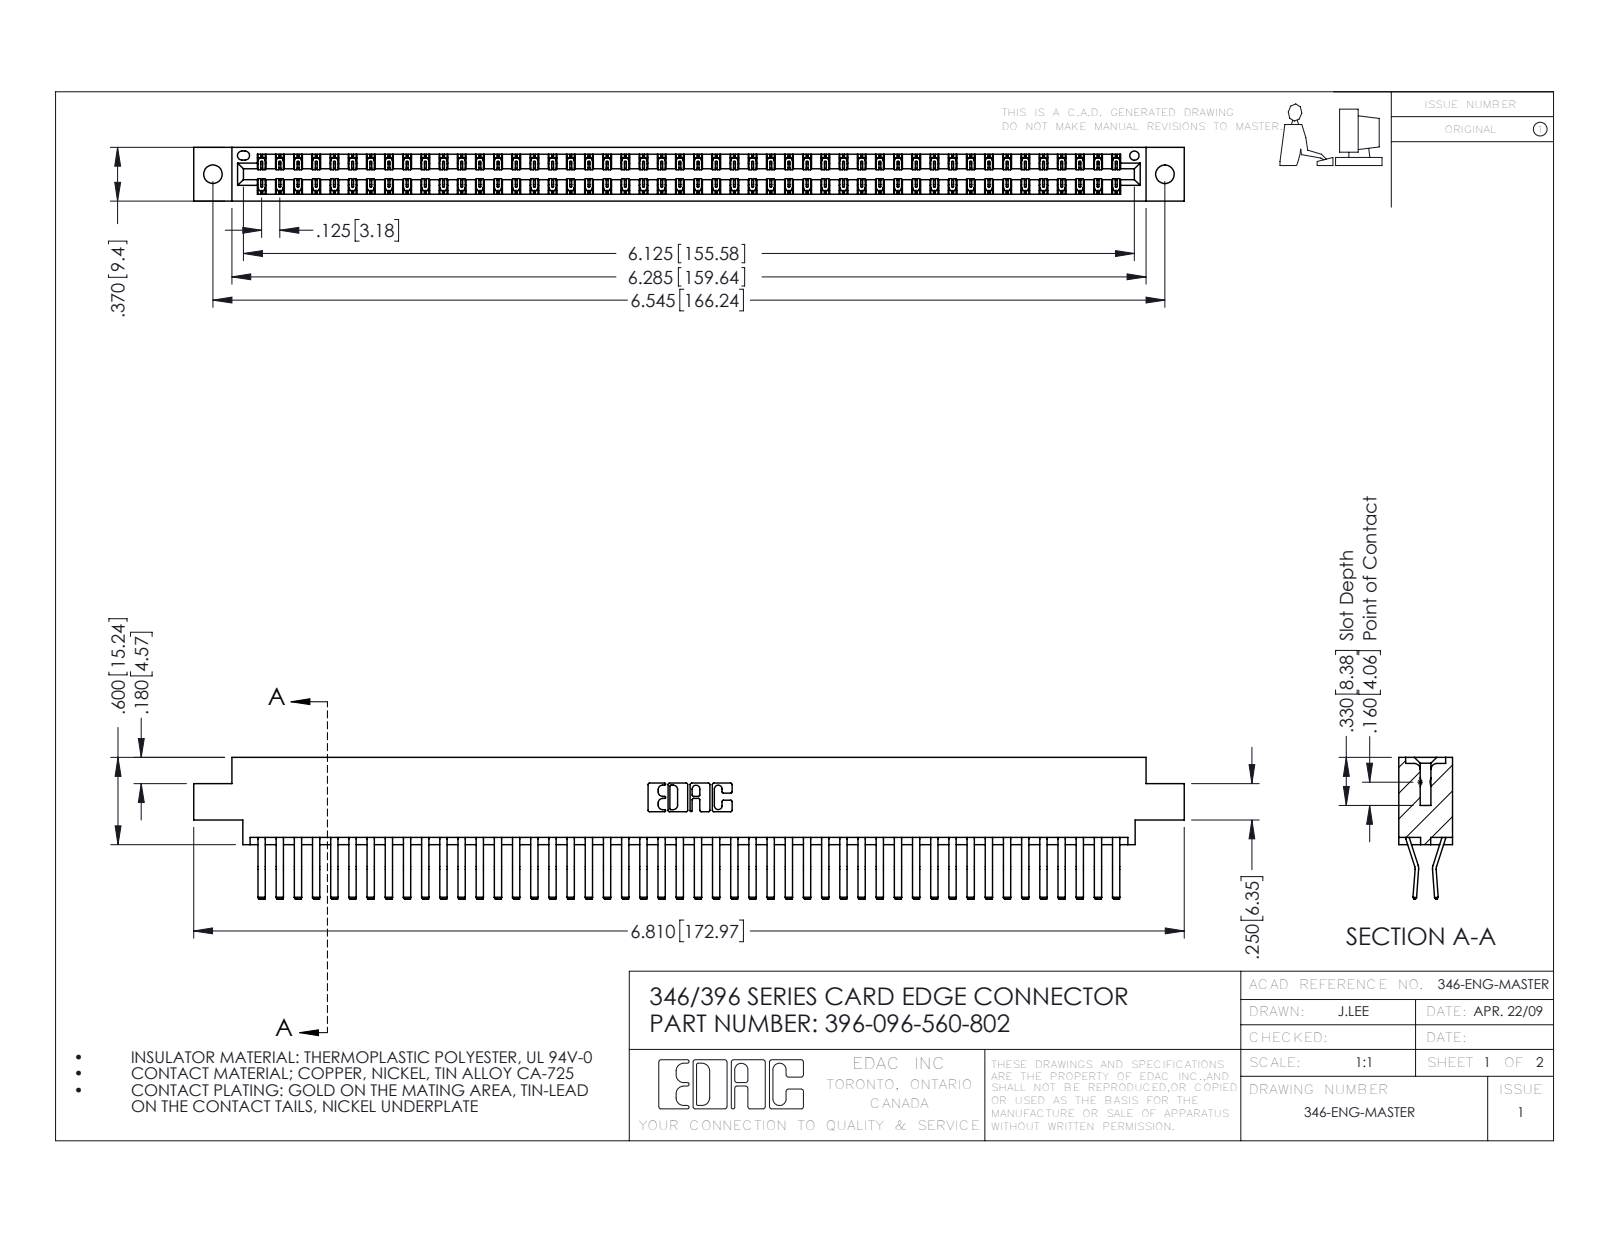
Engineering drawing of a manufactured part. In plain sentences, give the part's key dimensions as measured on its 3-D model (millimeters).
The part is named "346 Part_0.170 Offset - 0.128 Dia; 396-096-560-802; 345-292-001_560 Tail". Its 3-D file was written by "SolidWorks 2016 (CONFIG_CONTROL_DESIGN)". It is 97 solids with 5310 faces: 3440 planar, 1870 cylindrical and 0 other. Overall it measures 173 by 24.8 by 9.4 millimeters. Its volume is 17 350 cubic millimeters and its surface area 25 540 square millimeters. Round holes: 2 of diameter 3.3, 1 of diameter 1.6. Partial cylindrical surfaces (rounded edges, fillets, slot ends): 144 of radius 0.2, 22 of radius 0.3, 6 of radius 0.2, 6 of radius 0.8, 3 of radius 0.7, 2 of radius 0.3, 2 of radius 0.4, 2 of radius 0.6. The main face-to-face distances are 1.2, 8.2, 9.4, 0.6, 6.4, 1.8, 7.6, 7, 3.8, 5.6. The hole center spacings are 6.2, 160.9, 166.2.
